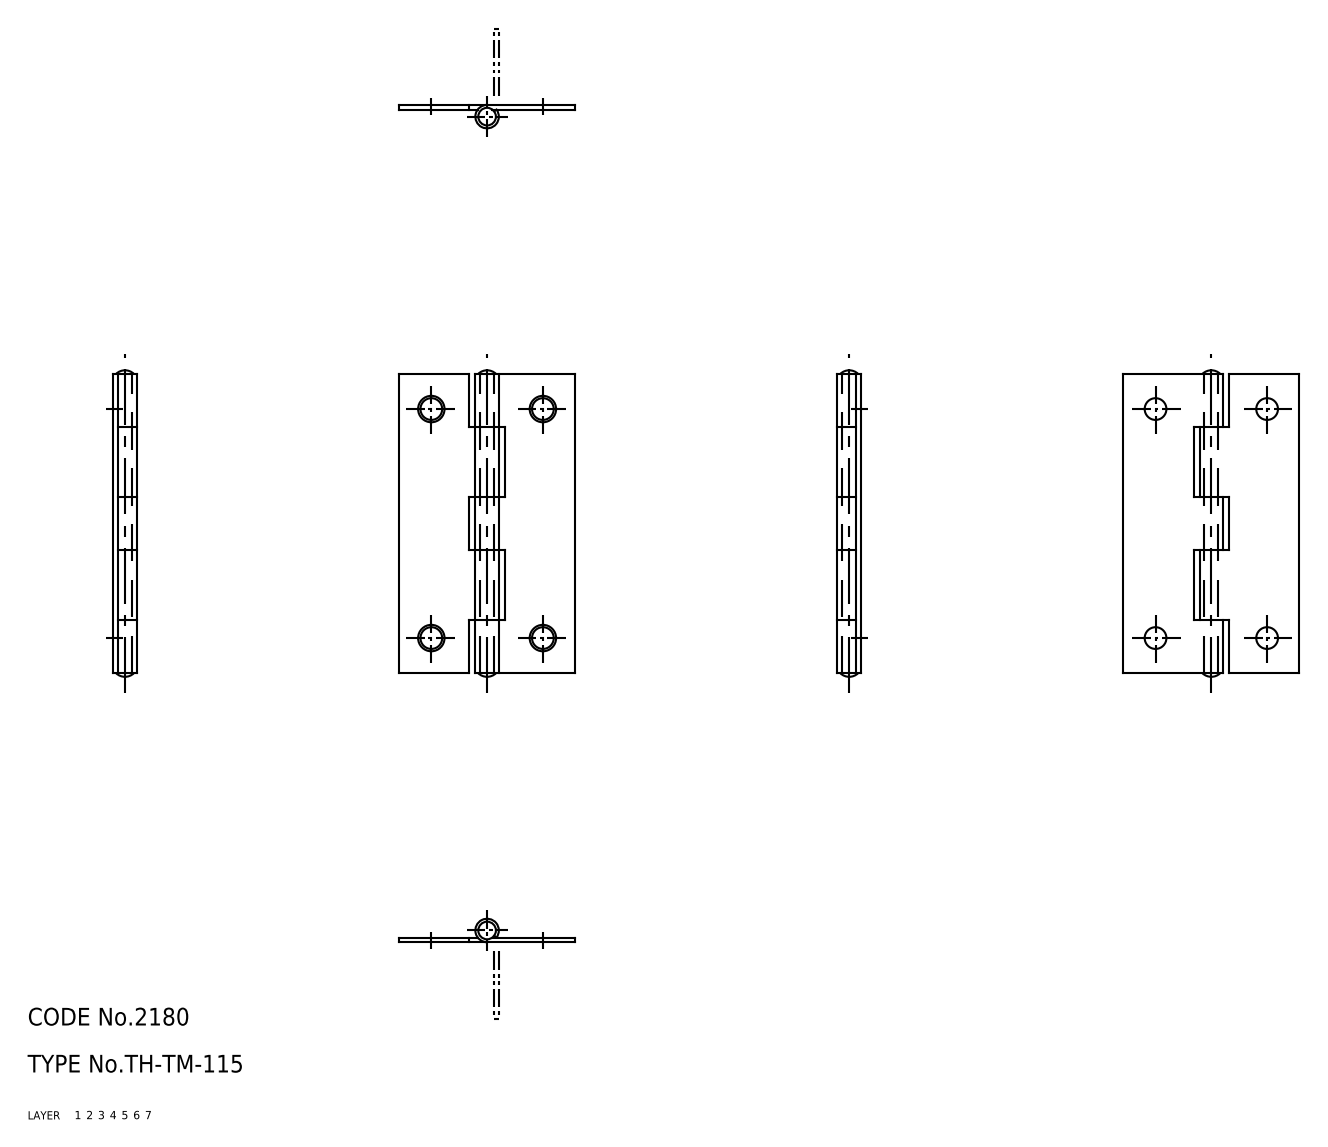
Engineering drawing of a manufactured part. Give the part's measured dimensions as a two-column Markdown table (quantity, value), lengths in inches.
| quantity | value |
| --- | --- |
| part name | 67112320; 67112333; 67112346 |
| STEP written by | CADfix (AUTOMOTIVE_DESIGN) |
| units | inches |
| bodies | 3 solids, 60 faces (0 planar, 0 cylindrical, 60 other) |
| overall size | 2.055 × 1.181 × 0.157 |
| volume | 0.1 in³ |
| surface area | 6.611 in² |
